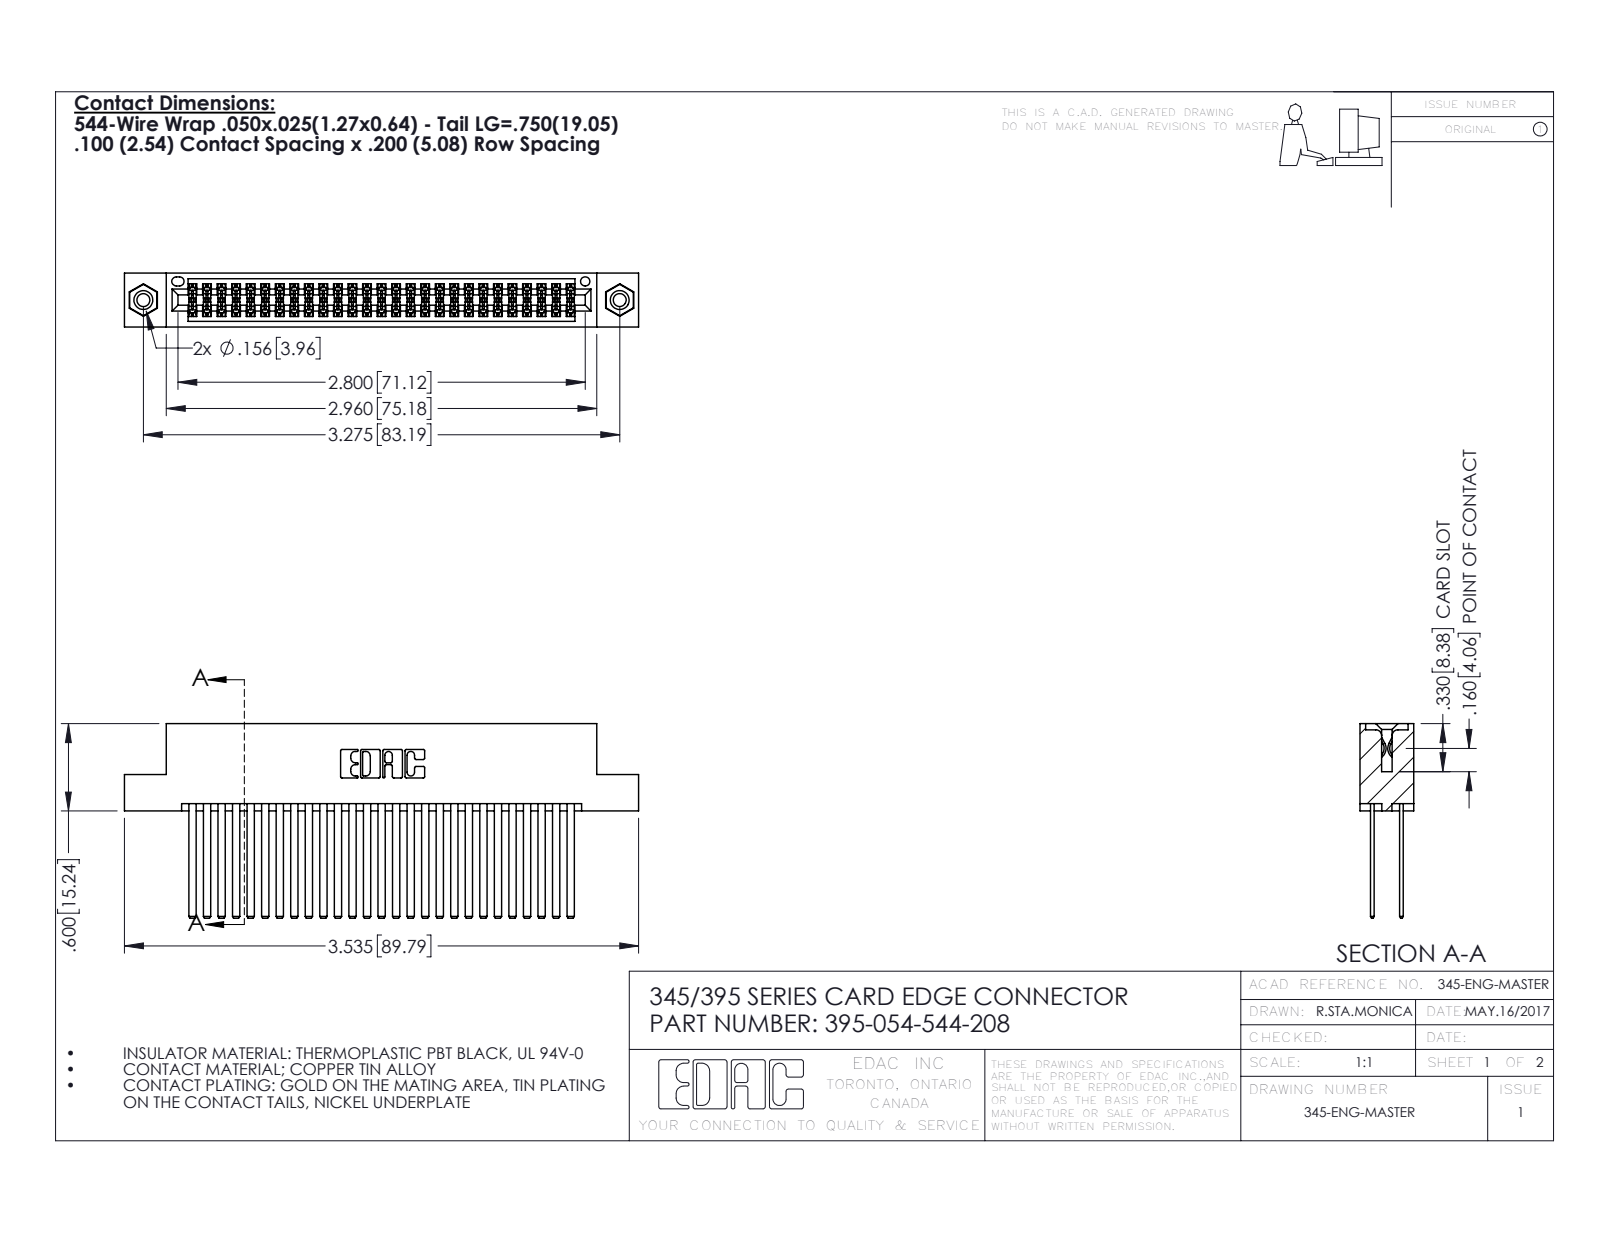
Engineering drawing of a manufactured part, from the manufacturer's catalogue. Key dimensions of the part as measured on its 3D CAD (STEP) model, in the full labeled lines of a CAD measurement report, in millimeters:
Part name (STEP PRODUCT): 345-292-001_345-293-144; 345-250-001_345-250-003-102; 345 Part_Flush Mounting Lugs - 0.156 Dia-TI; 395-054-544-208
STEP written by: SolidWorks 2016 (CONFIG_CONTROL_DESIGN)
Units: millimetres
Bodies: 57 solids, 2562 faces (1678 planar, 868 cylindrical, 16 other)
Overall size (bounding box): 89.8 × 34 × 9.4
Volume: 9 340 mm³ · Surface area: 15 740 mm²
Round holes (diameter × count): ⌀2.3 ×2, ⌀3.2 ×2, ⌀4 ×2, ⌀1.6 ×1
Round bosses / shafts (diameter × count): ⌀3.9 ×2
Partial cylindrical surfaces — rounded edges, fillets, slot ends (radius × count): R0.2 ×81, R0.3 ×22, R0.2 ×6, R0.8 ×6, R0.7 ×3, R0.4 ×2, R0.5 ×2, R0.6 ×2
Main face-to-face distances: 5.1, 1.8, 7.6, 0.6, 2.5, 6.9, 5.7, 4.4, 9.4, 1.3
Hole centre spacings: 6.9, 77.2, 83.2
